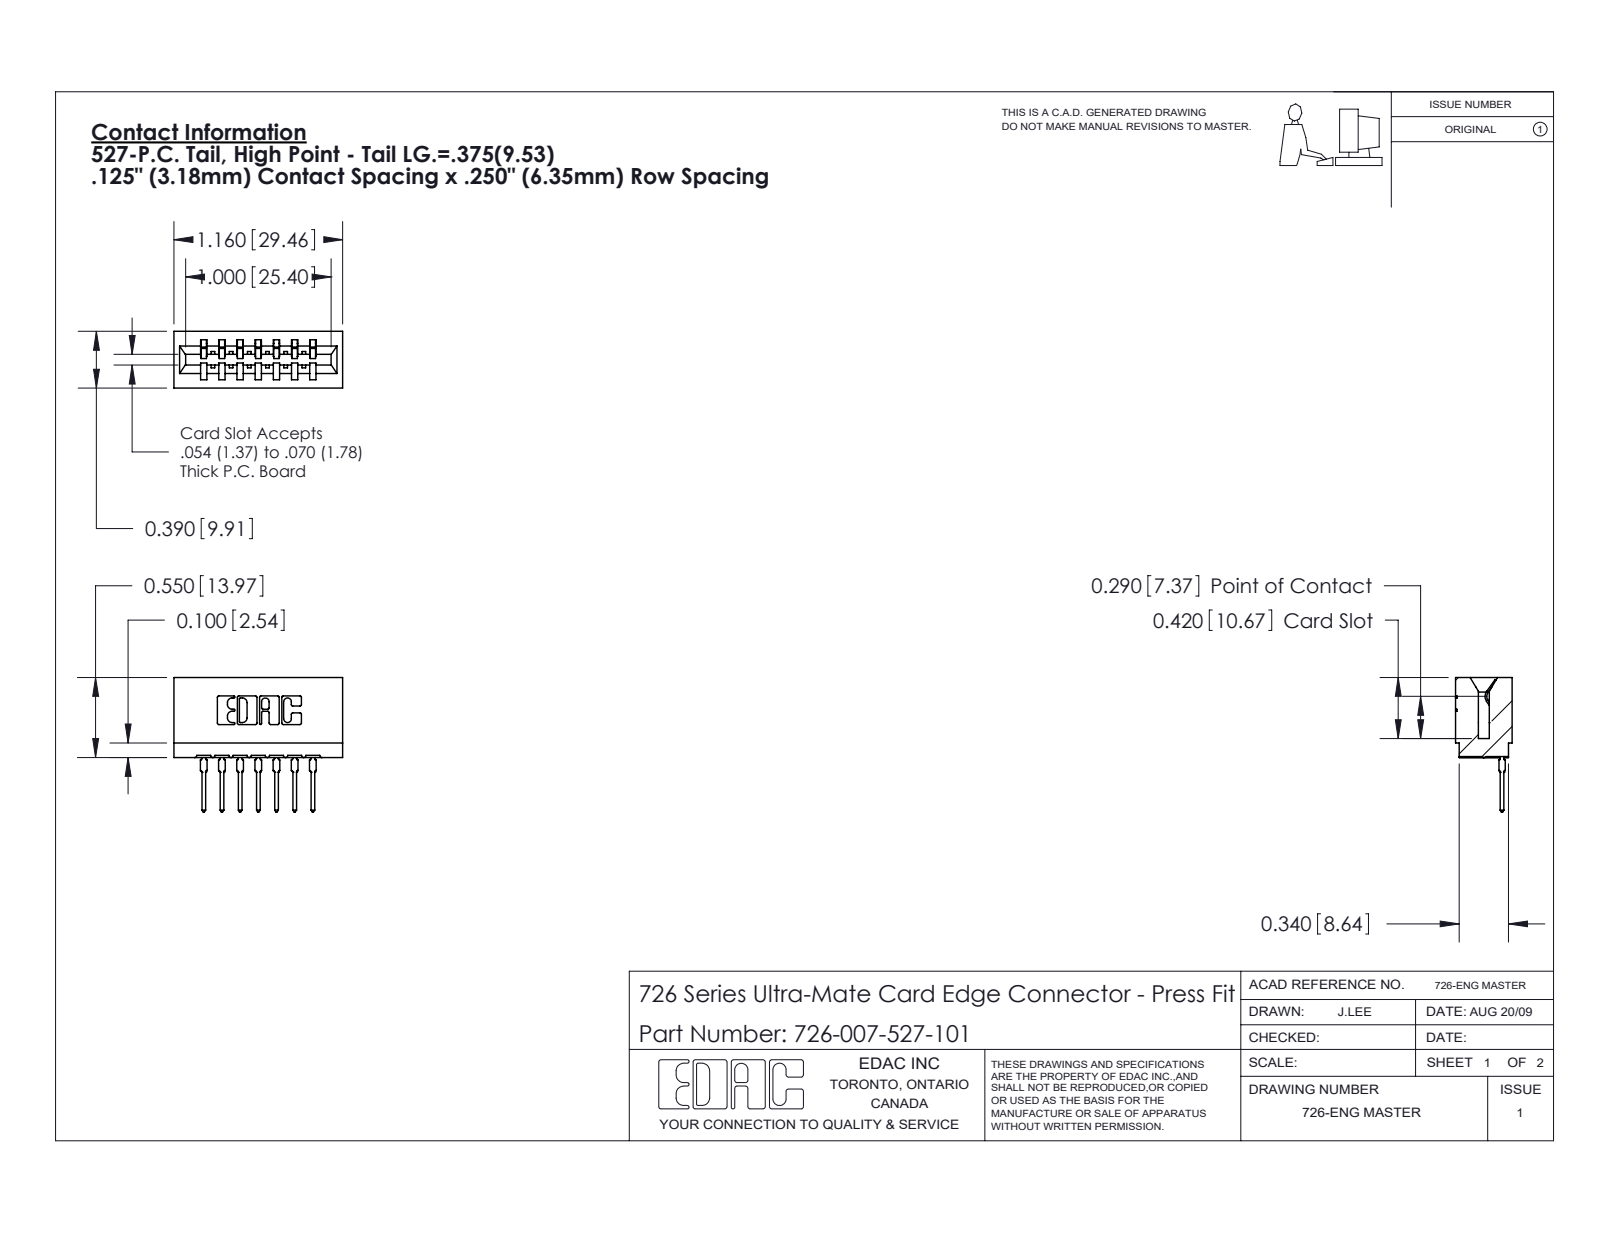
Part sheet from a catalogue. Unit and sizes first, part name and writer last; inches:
Units: inches
Overall size (bounding box): 1.16 × 0.924 × 0.39
Partial cylindrical surfaces — rounded edges, fillets, slot ends (radius × count): R0.01 ×22, R0.021 ×14, R0.015 ×8, R0.007 ×6, R0.031 ×6, R0.005 ×4, R0.011 ×4, R0.026 ×3
Main face-to-face distances: 0.25, 0.042, 0.333, 0.057, 0.125, 0.125, 0.5, 0.292, 0.208, 0.39
Volume: 0.173 in³ · Surface area: 5.977 in²
Bodies: 8 solids, 853 faces (496 planar, 175 cylindrical, 182 other)
Part name (STEP PRODUCT): 746-292-001_527; 726-007-527-101; 726 Part_.515 Slot Depth - 01
STEP written by: SolidWorks 2020 (CONFIG_CONTROL_DESIGN)
